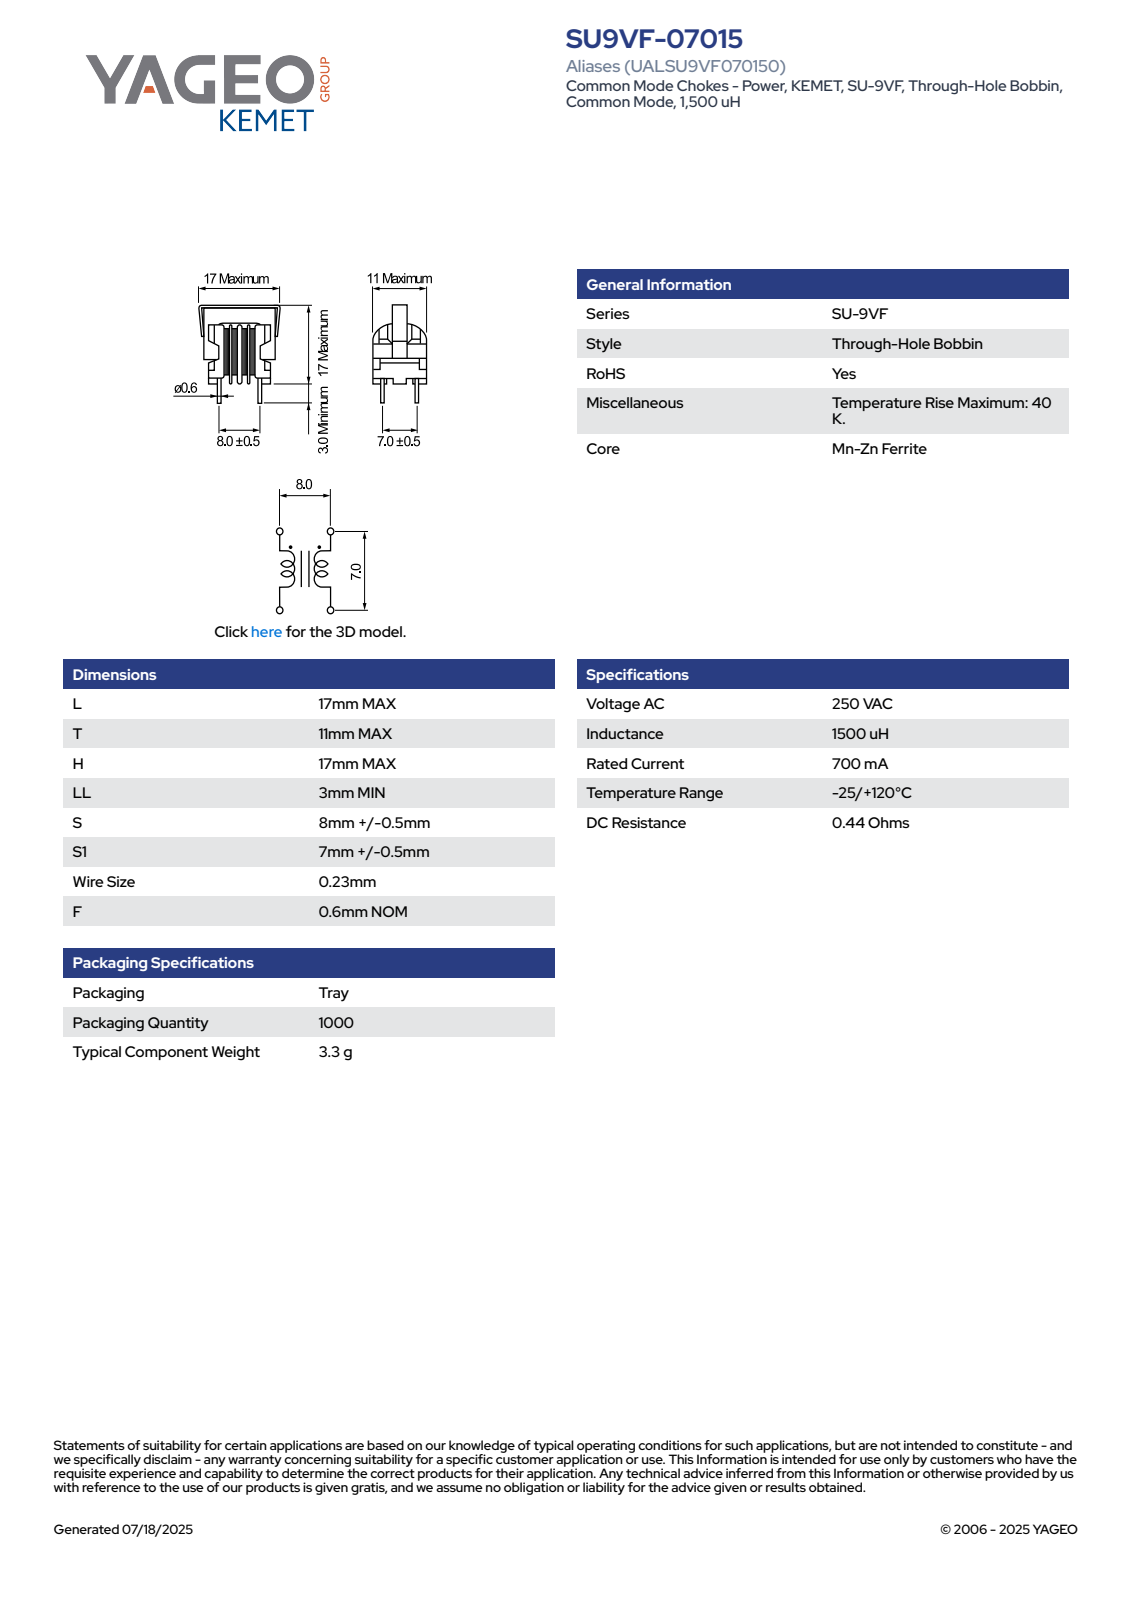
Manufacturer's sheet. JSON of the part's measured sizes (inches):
{"part_name": "SU9VF(MAX-LOGO)", "step_written_by": "SolidWorks 2018 (AUTOMOTIVE_DESIGN)", "units": "inches", "bodies": {"solids": 1, "faces": 485, "planar": 229, "cylindrical": 168, "other": 88}, "overall_size": [0.846, 0.669, 0.433], "volume_in3": 0.065, "surface_area_in2": 2.711, "round_bosses_or_shafts": [[0.024, 4]], "partial_cylinders_radius": [[0.006, 64], [0.012, 50], [0.02, 12], [0.008, 4], [0.039, 2], [0.079, 2], [0.138, 2]], "face_to_face_distances": [0.144, 0.11, 0.031, 0.145, 0.08, 0.049, 0.096, 0.065, 0.085, 0.343]}
